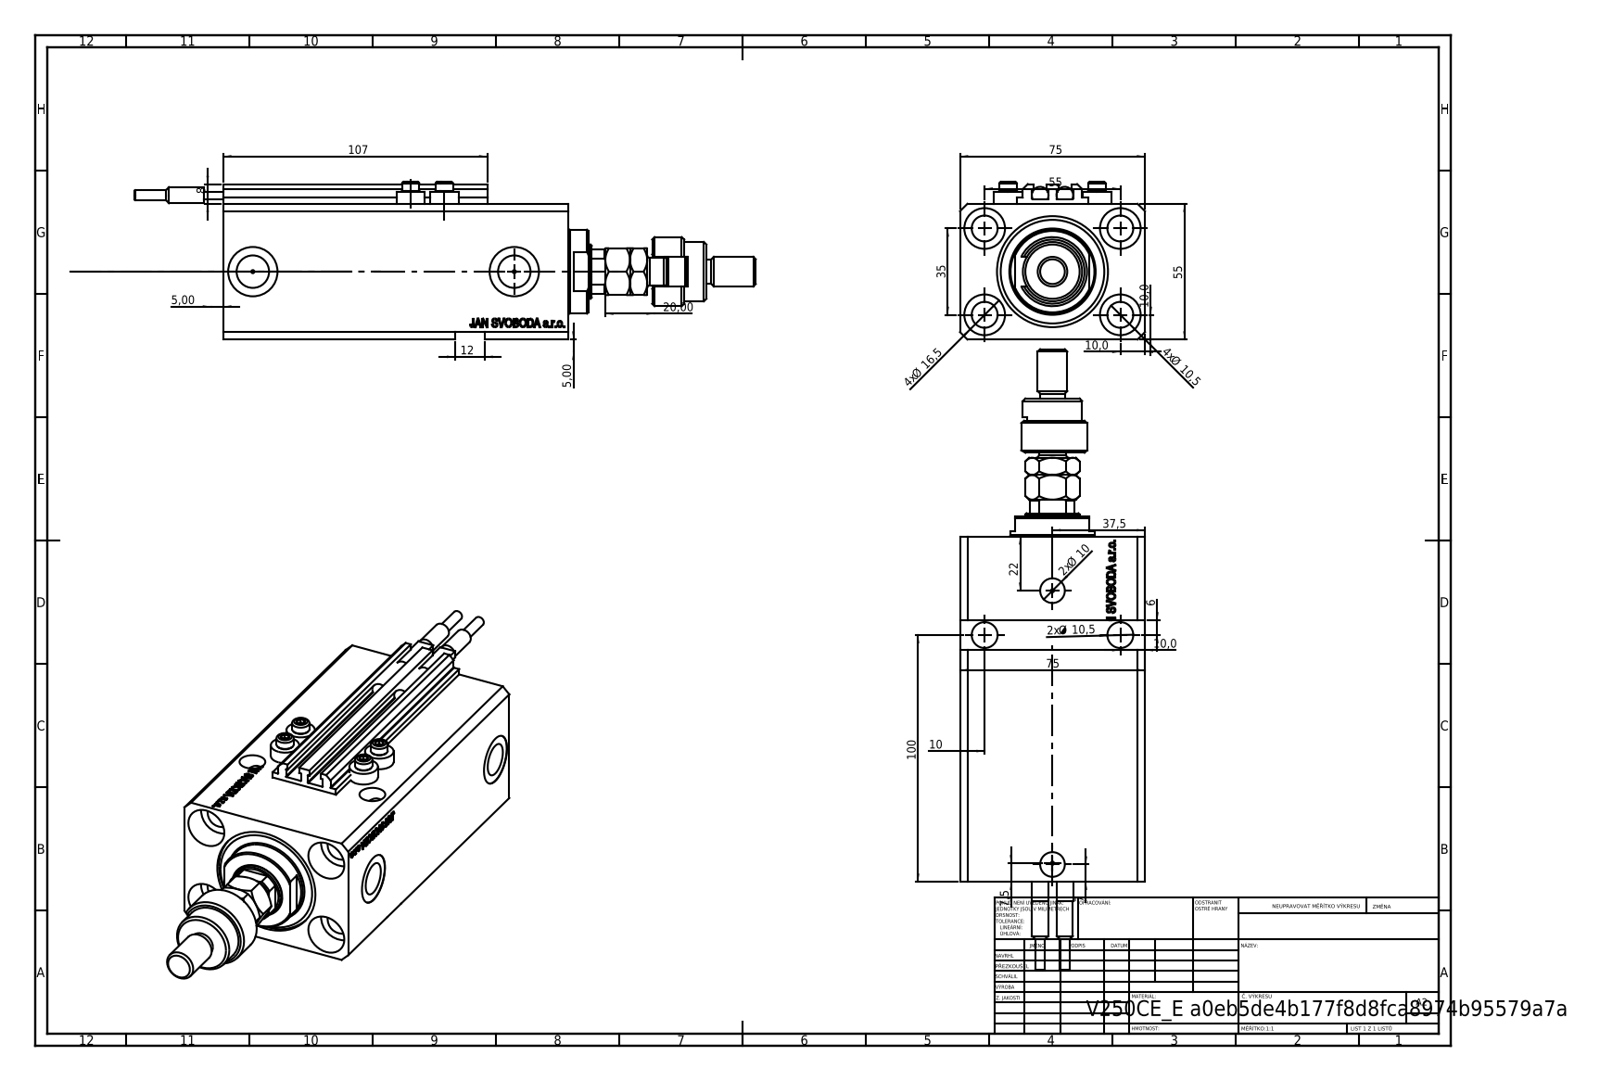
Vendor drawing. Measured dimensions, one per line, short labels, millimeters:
name: SWITCH_V250CE; MFA; FEMALE_PART_FOR_DFA; V250CE_E_Body (+3 more)
written by: SolidWorks 2019 (CONFIG_CONTROL_DESIGN)
unit: mm
bodies: 12 solids, 1217 faces (578 planar, 163 cylindrical, 476 other)
size: 251.9 × 75 × 64
volume: 509 476 mm³; area: 127 382 mm²
holes: 7× ⌀10.5, 4× ⌀1.25, 4× ⌀4, 4× ⌀16.5, 2× ⌀10, 2× ⌀13.16, 2× ⌀20, 1× ⌀22, 1× ⌀32, 1× ⌀45
bosses: 4× ⌀11.6, 4× ⌀7, 2× ⌀6.8, 2× ⌀6.5, 2× ⌀4, 1× ⌀34, 1× ⌀28, 1× ⌀24
rounds: 10× R0.2, 1× R9.75, 1× R10.5
face distances: 55, 75, 3, 57, 9.9, 27.1, 140, 8, 112.9, 2
hole spacings: 32.6, 55, 13.6, 14.09, 25.81, 32.87, 33.62, 35
